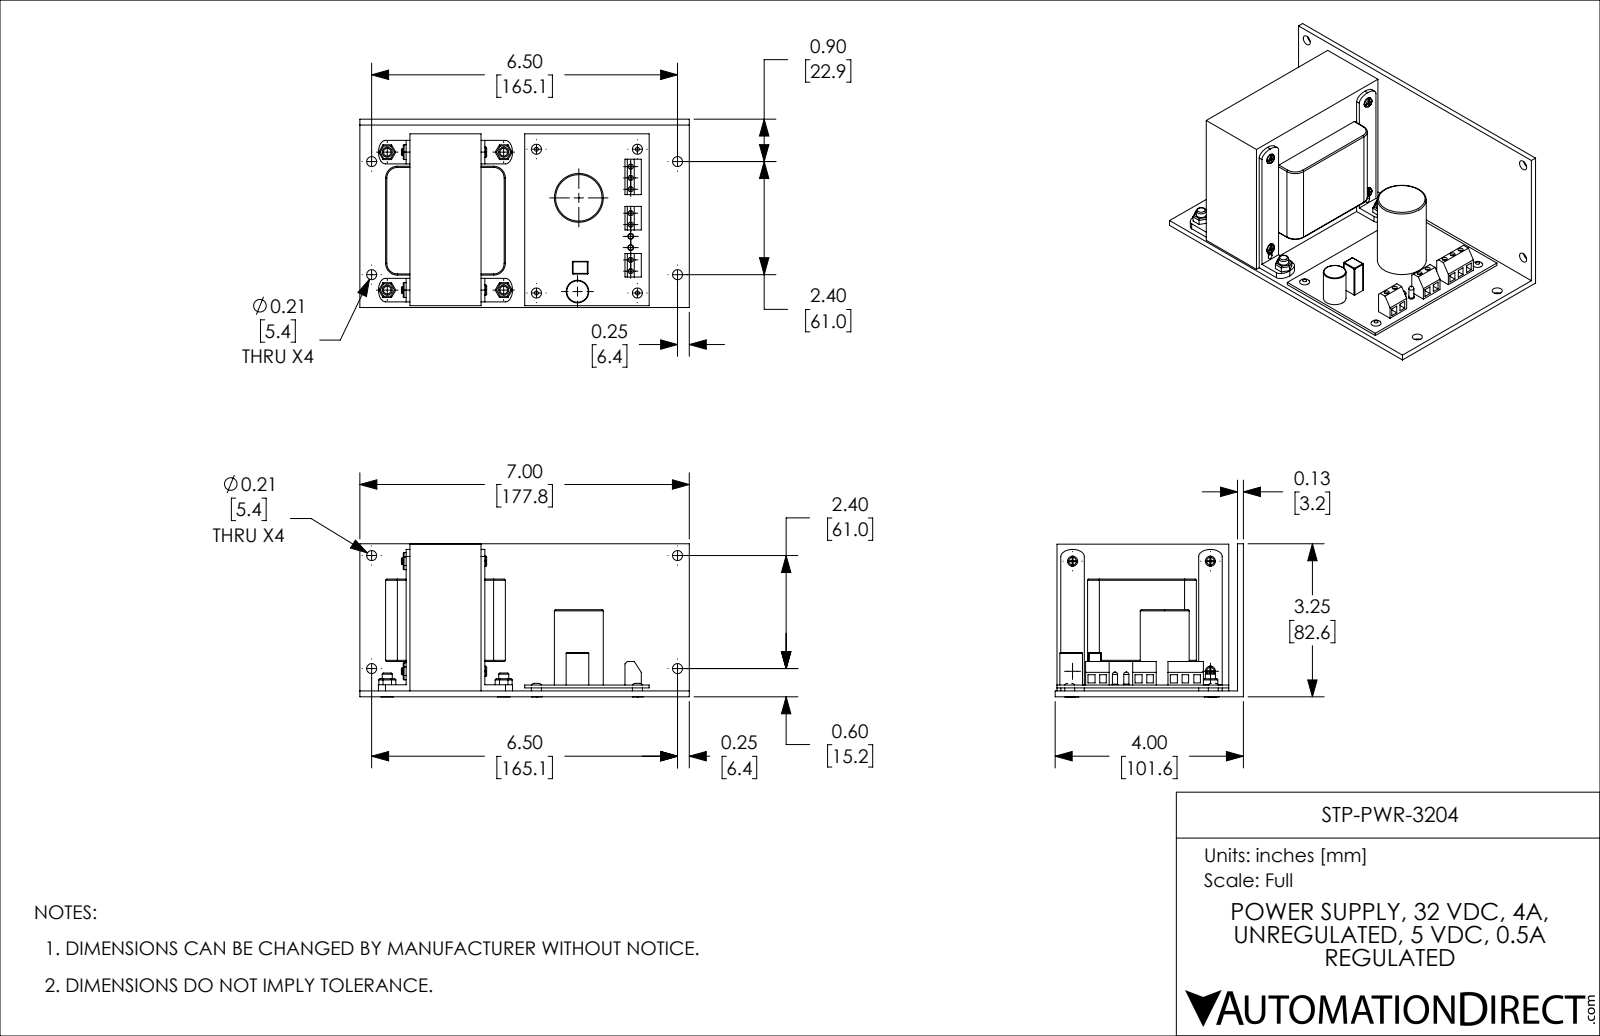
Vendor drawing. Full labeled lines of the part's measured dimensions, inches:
Part name (STEP PRODUCT): STP-PWR-3204
STEP written by: SolidWorks 2023 (CONFIG_CONTROL_DESIGN)
Units: inches
Bodies: 1 solid, 683 faces (381 planar, 222 cylindrical, 80 other)
Overall size (bounding box): 7 × 4 × 3.251
Volume: 30.54 in³ · Surface area: 177.8 in²
Round holes (diameter × count): ⌀0.213 ×8, ⌀0.108 ×7, ⌀0.213 ×4
Round bosses / shafts (diameter × count): ⌀0.213 ×8, ⌀0.257 ×4, ⌀0.144 ×4, ⌀0.123 ×2, ⌀0.108 ×2, ⌀1.038 ×1, ⌀0.481 ×1
Partial cylindrical surfaces — rounded edges, fillets, slot ends (radius × count): R0.025 ×28, R0.019 ×20, R0.012 ×8, R0.055 ×4, R0.25 ×4
Main face-to-face distances: 0.125, 0.125, 0.065, 0.19, 0.25, 0.06, 3.243, 3.117, 3.052, 2.993
Hole centre spacings: 6.5, 0.24, 0.75, 0.99, 1.74, 2.4, 2.402, 2.474
